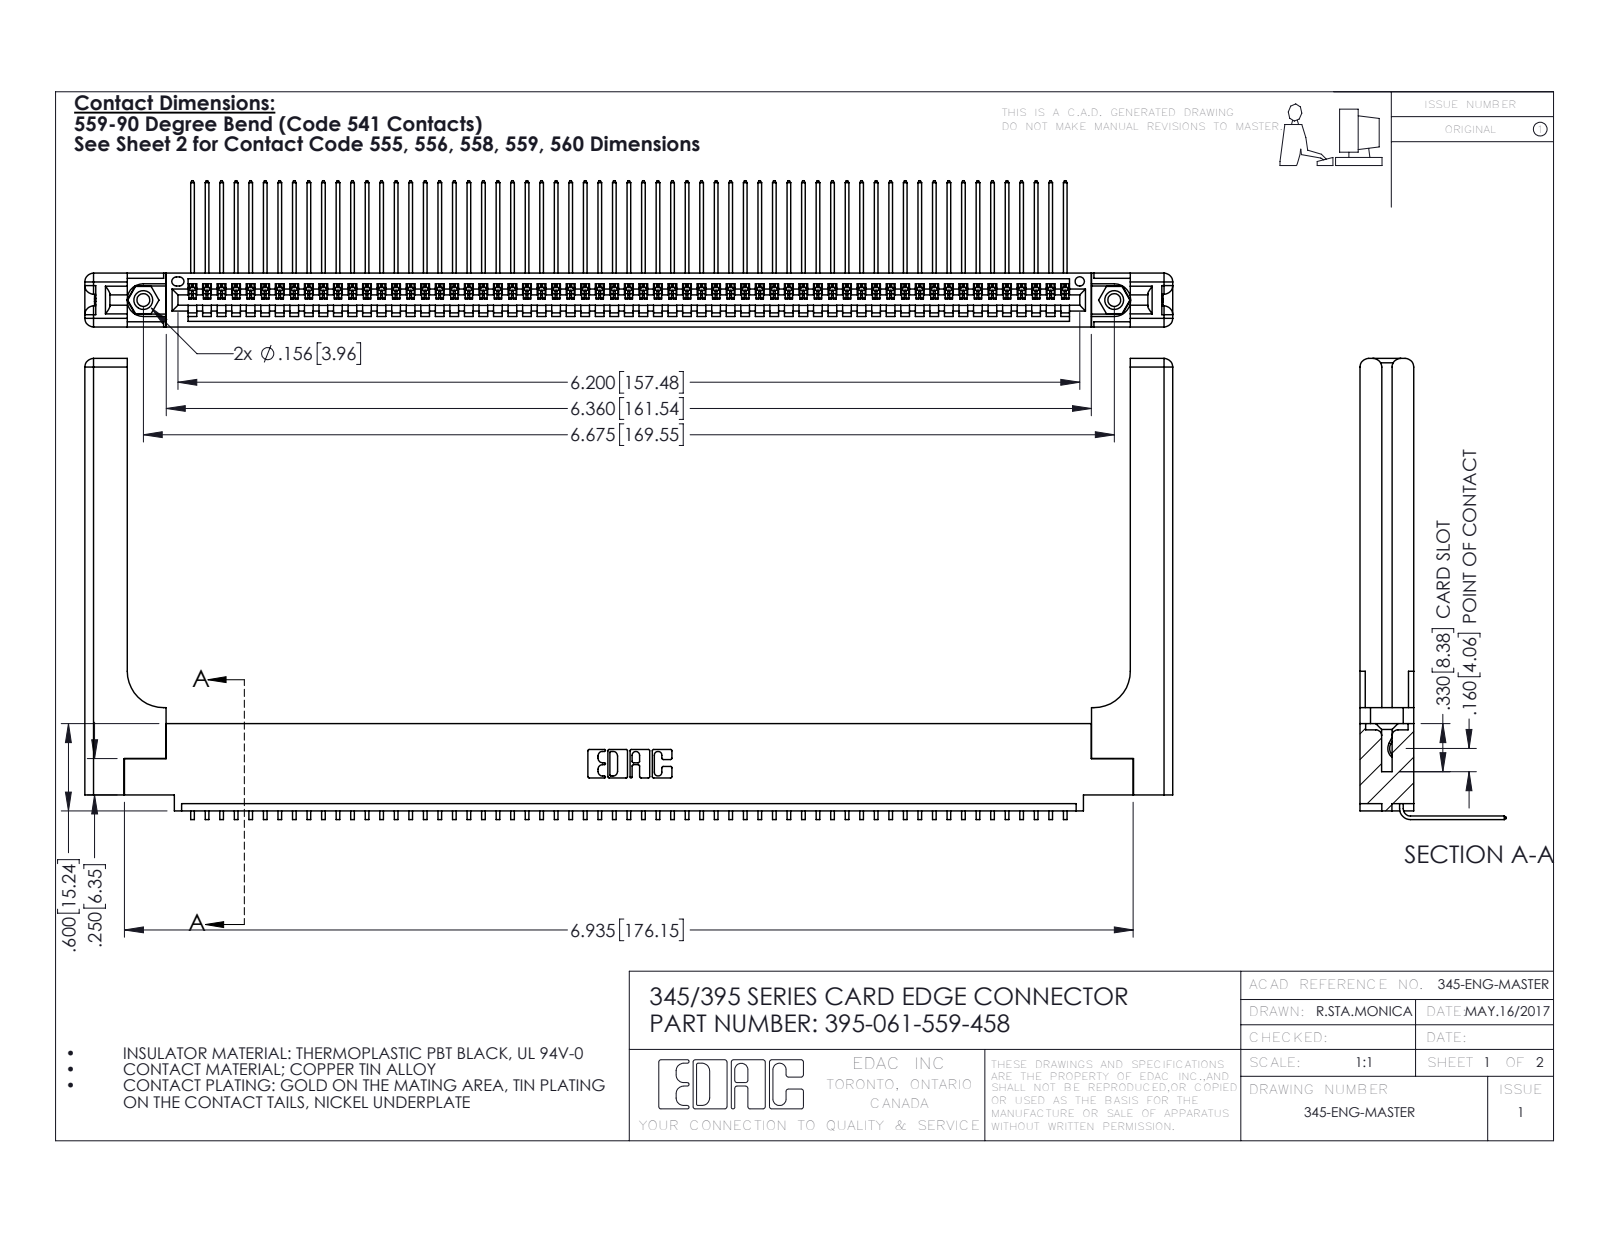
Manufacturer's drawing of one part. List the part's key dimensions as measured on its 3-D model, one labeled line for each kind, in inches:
Part name (STEP PRODUCT): 345 Part_0.110 Offset - 0.156 Dia-TH; 345-220-058_345-220-058; 345-250-001_345-250-001-102; 395-061-559-458 (+1 more)
STEP written by: SolidWorks 2016 (CONFIG_CONTROL_DESIGN)
Units: inches
Bodies: 66 solids, 4046 faces (2794 planar, 1192 cylindrical, 60 other)
Overall size (bounding box): 7.479 × 3.169 × 1.005
Volume: 1.637 in³ · Surface area: 48.36 in²
Round holes (diameter × count): ⌀0.089 ×2, ⌀0.125 ×2, ⌀0.156 ×2, ⌀0.064 ×1
Round bosses / shafts (diameter × count): ⌀0.155 ×2
Partial cylindrical surfaces — rounded edges, fillets, slot ends (radius × count): R0.006 ×122, R0.01 ×22, R0.06 ×16, R0.007 ×6, R0.031 ×6, R0.026 ×3, R0.03 ×2, R0.031 ×2
Main face-to-face distances: 0.072, 0.37, 0.298, 0.098, 0.272, 0.025, 0.2, 0.225, 0.148, 0.15
Hole centre spacings: 0.27, 6.439, 6.675
